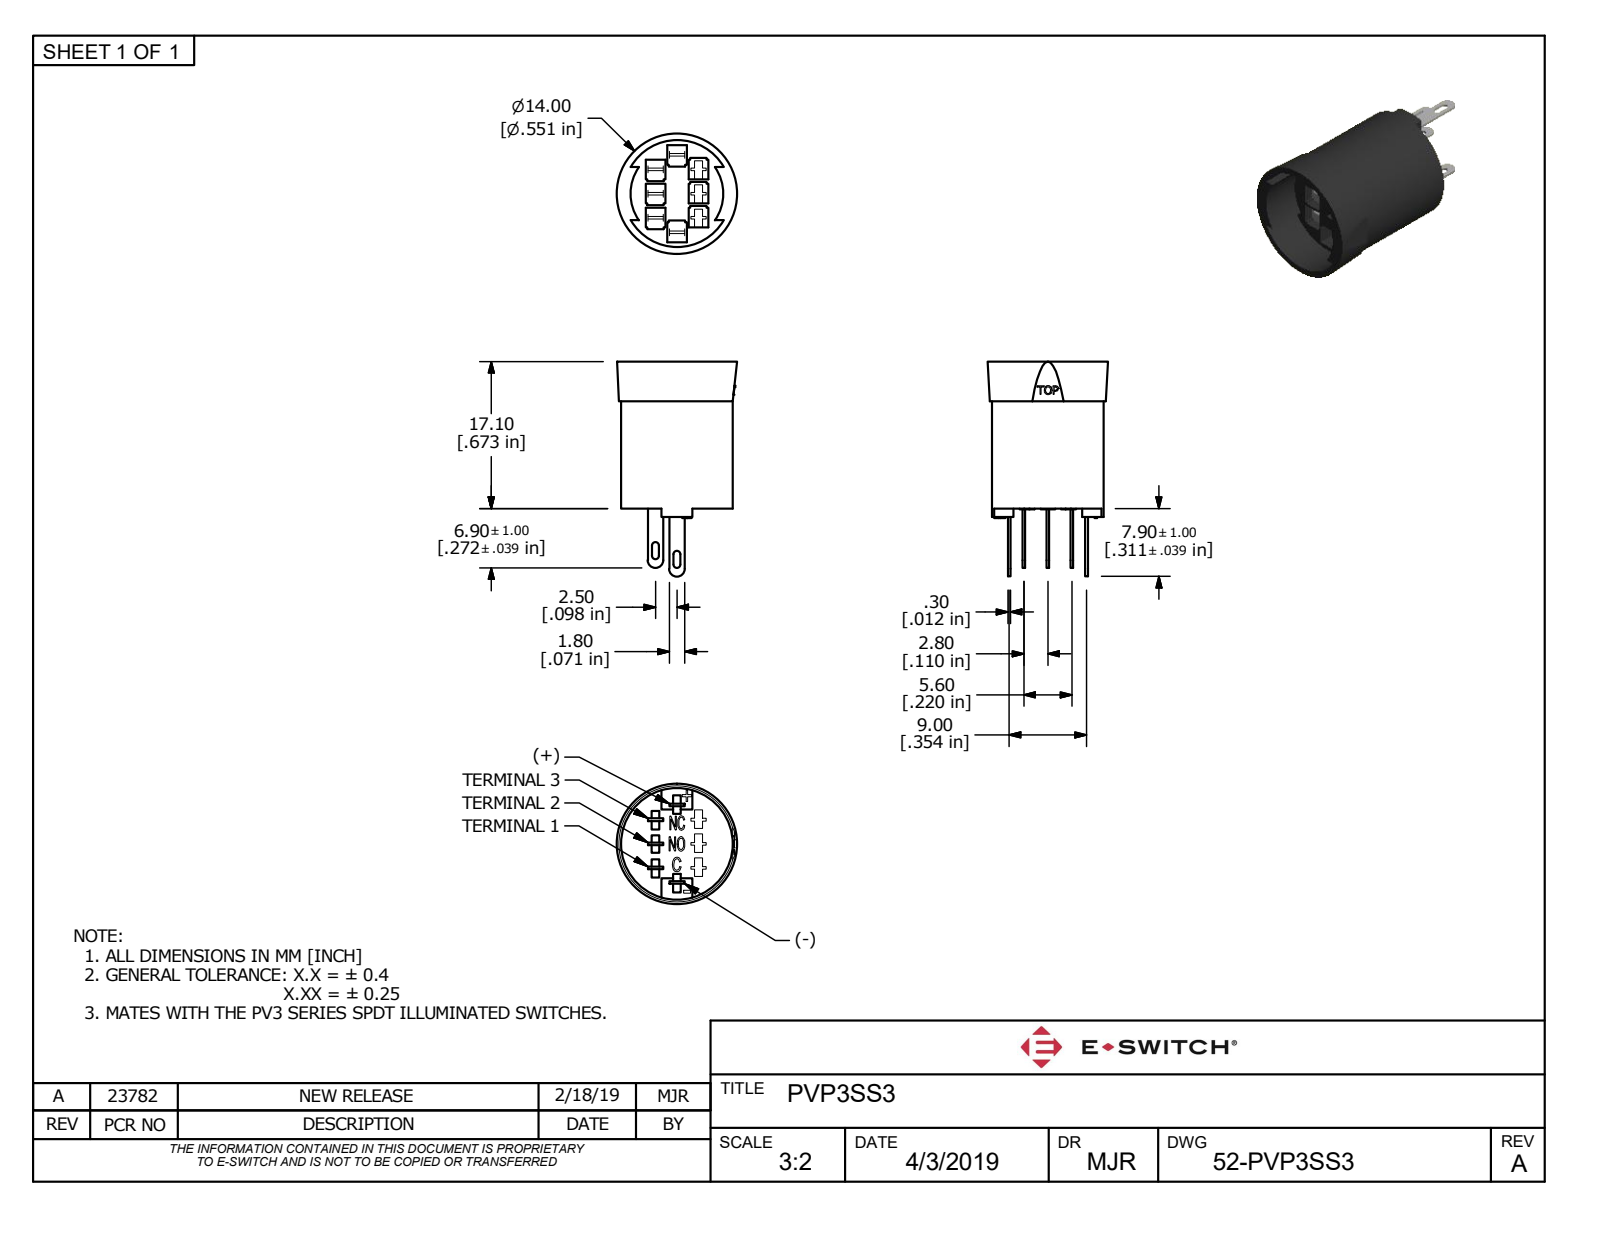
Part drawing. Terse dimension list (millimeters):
name: PVP3SS3
written by: Autodesk Inventor 2018 (AP242_MANAGED_MODEL_BASED_3D_ENGINEERING_MIM_LF)
unit: mm
bodies: 1 solid, 368 faces (288 planar, 30 cylindrical, 50 other)
size: 25 × 14 × 14
volume: 1 599 mm³; area: 1 999 mm²
bosses: 1× ⌀13
rounds: 10× R0.25, 4× R0.4, 2× R0.9, 2× R6.25, 1× R5.4
face distances: 2.8, 2.5, 1.3, 1, 4.1, 1.5, 1.8, 1.6, 7.3, 4.5
